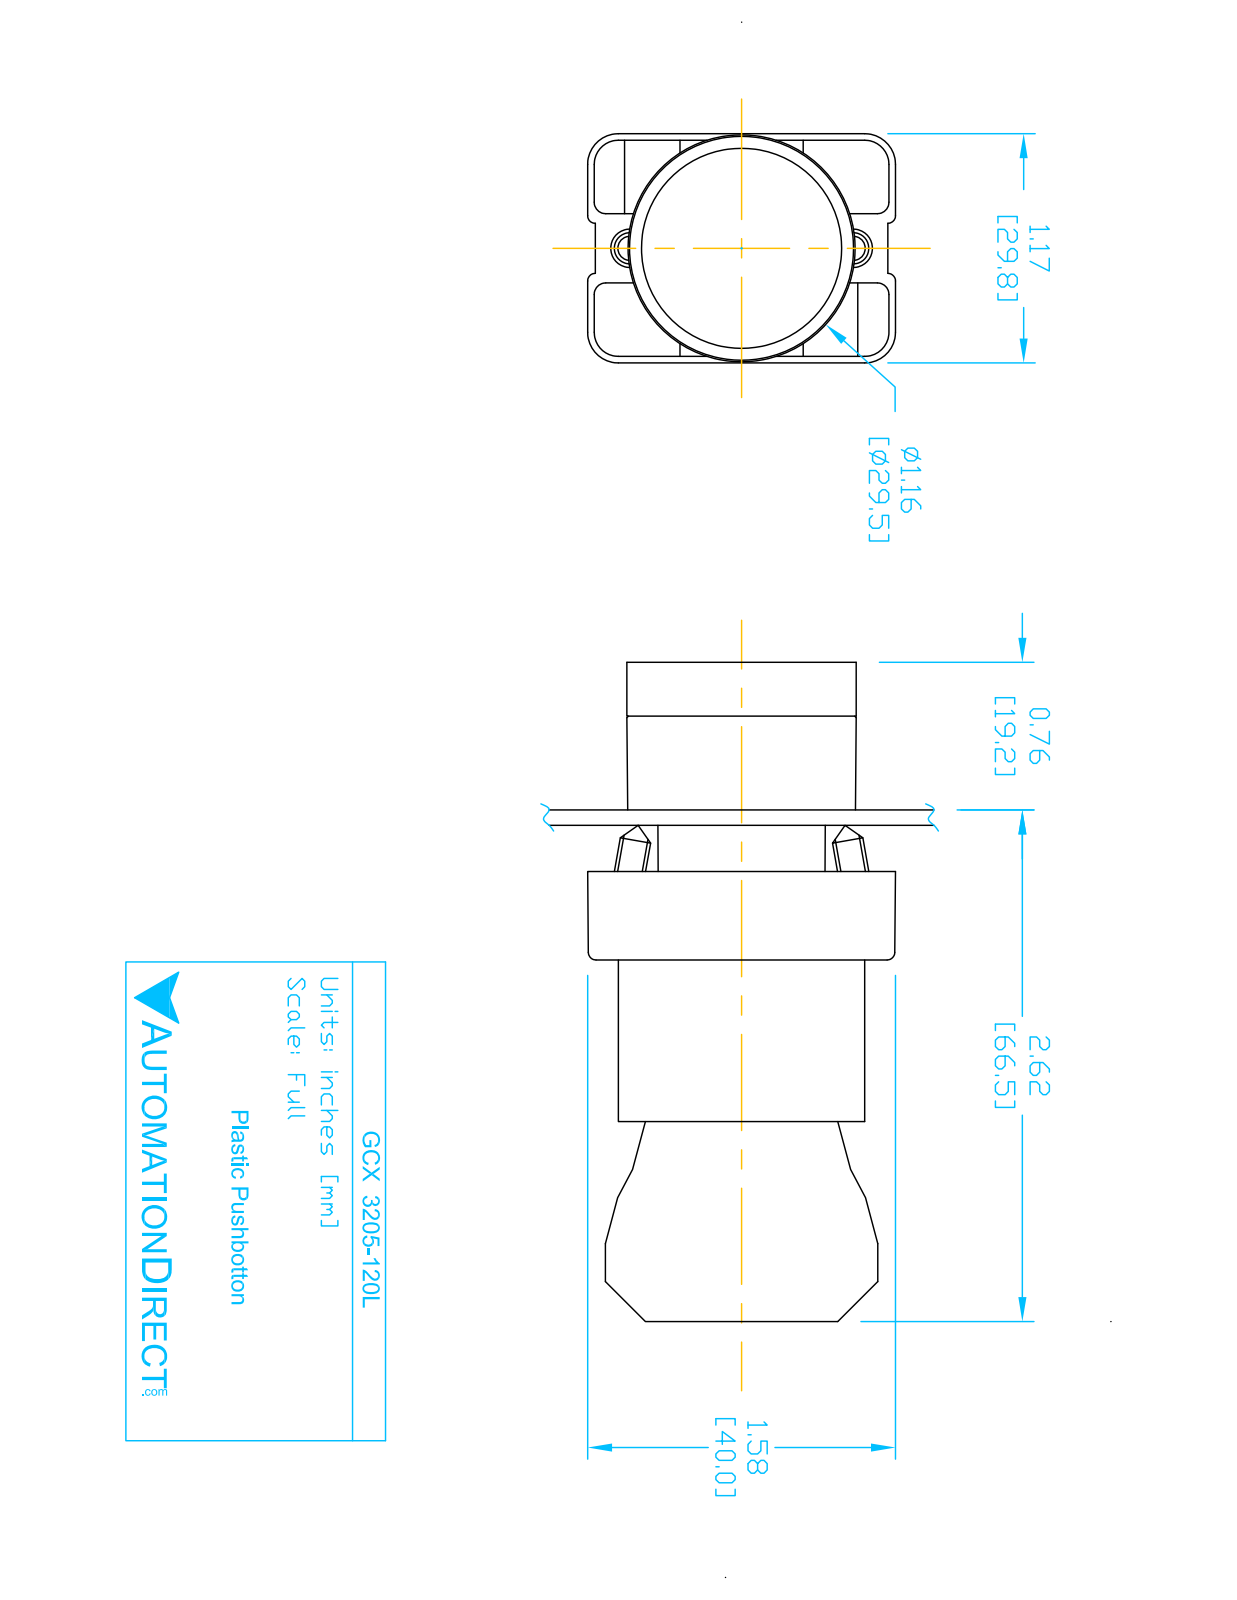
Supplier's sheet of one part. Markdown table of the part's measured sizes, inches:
| quantity | value |
| --- | --- |
| part name | ecx1040; GCX3205L OPERATOR; ECX3029-2; GCX3205-120L (+1 more) |
| STEP written by | SolidWorks 2016 (AUTOMOTIVE_DESIGN) |
| units | inches |
| bodies | 8 solids, 431 faces (252 planar, 148 cylindrical, 31 other) |
| overall size | 3.319 × 1.581 × 1.177 |
| volume | 2.794 in³ |
| surface area | 38.77 in² |
| round holes (diameter × count) | 0.079 × 2, 0.124 × 2, 0.13 × 2, 0.087 × 1, 0.197 × 1, 0.469 × 1, 0.878 × 1, 0.888 × 1, 1.024 × 1 |
| round bosses / shafts (diameter × count) | 0.157 × 4, 1.175 × 1, 1.004 × 1, 0.945 × 1, 0.856 × 1, 0.78 × 1, 0.504 × 1 |
| partial cylindrical surfaces (radius × count) | 0.059 × 24, 0.041 × 12, 0.124 × 12, 0.157 × 12, 0.039 × 8, 0.128 × 2, 0.02 × 1, 0.063 × 1 |
| main face-to-face distances | 0.827, 0.579, 2.02, 1.193, 1.171, 0.276, 2.295, 1.469, 0.031, 0.033 |
| hole center spacings | 0.236, 0.544, 0.472, 0.49 |
